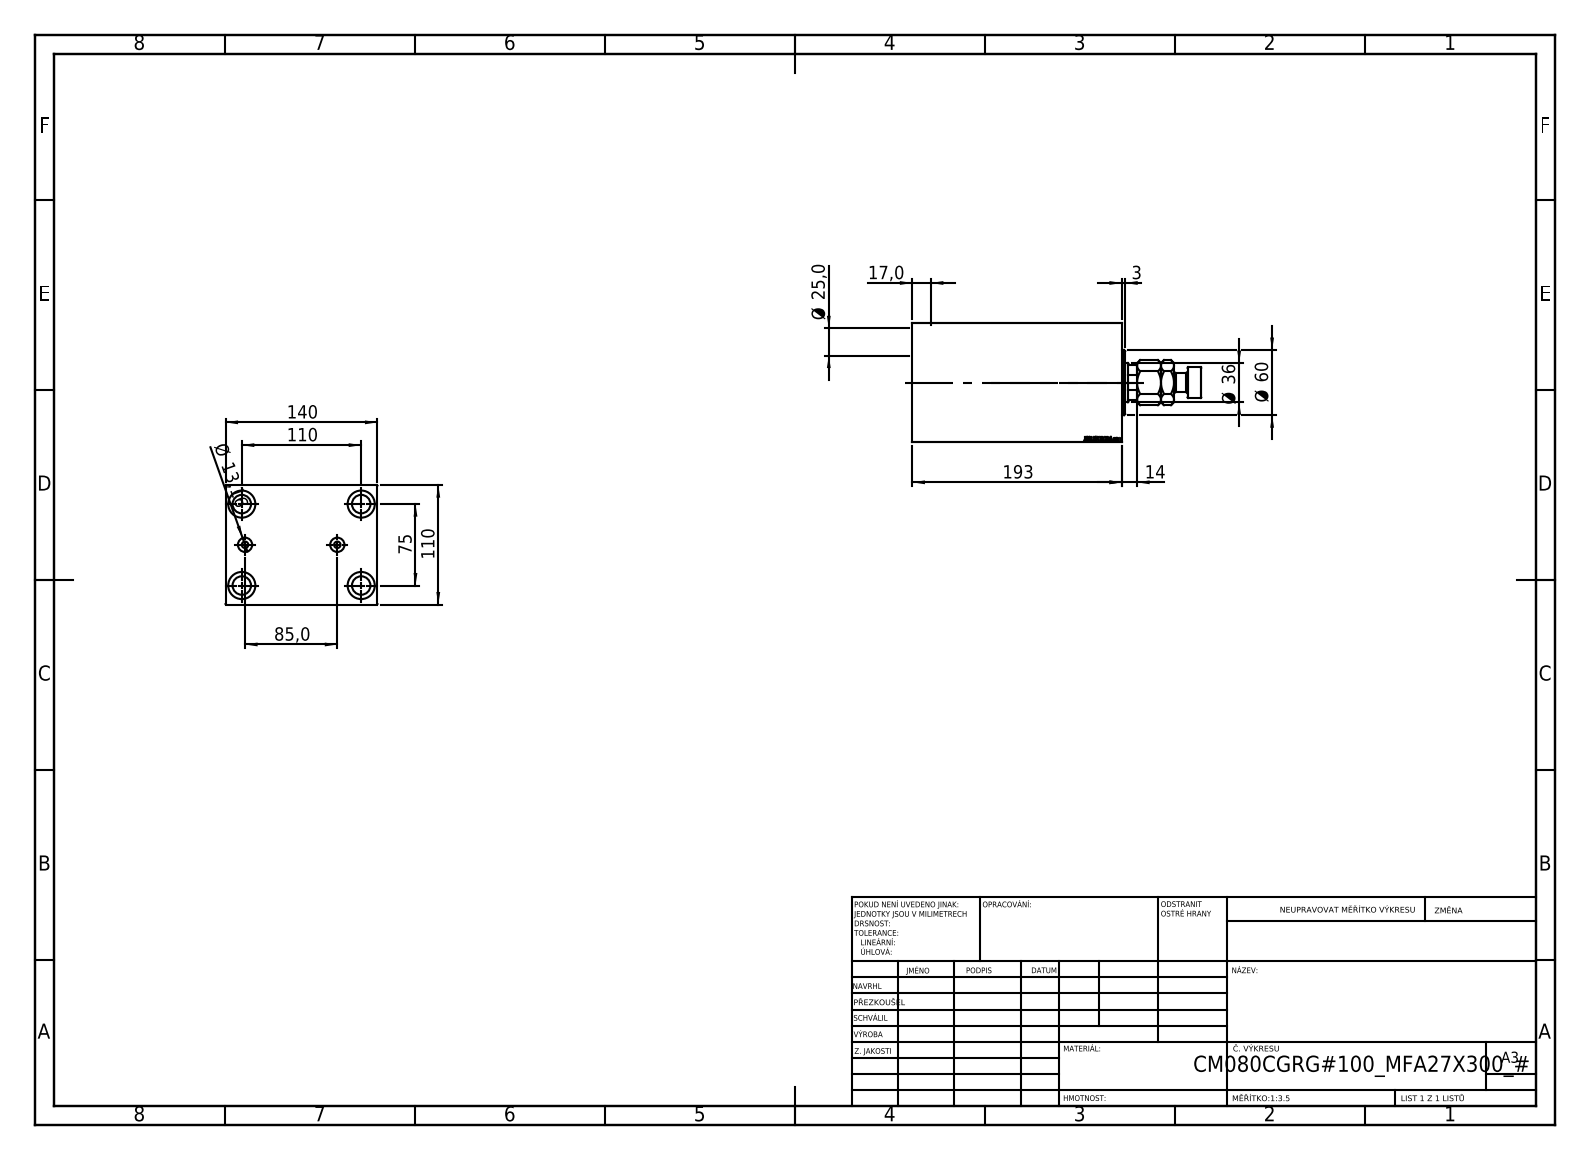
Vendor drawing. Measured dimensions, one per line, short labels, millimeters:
name: V450CM_VC_B; MFA; V450CM_C_Body; V450CM_C_VCP
written by: SolidWorks 2019 (CONFIG_CONTROL_DESIGN)
unit: mm
bodies: 4 solids, 912 faces (424 planar, 62 cylindrical, 426 other)
size: 266 × 140 × 110
volume: 2 401 000 mm³; area: 284 013 mm²
holes: 4× ⌀17, 4× ⌀25, 2× ⌀6, 2× ⌀13.16, 1× ⌀25.5, 1× ⌀36, 1× ⌀39.5, 1× ⌀80, 1× ⌀82, 1× ⌀87
bosses: 1× ⌀60, 1× ⌀28, 1× ⌀18
rounds: 1× R17.5
face distances: 110, 140, 193, 172, 21, 14, 179, 158, 100, 114
hole spacings: 66.57, 37.62, 43.48, 75, 95.66, 110, 113.38, 133.14
